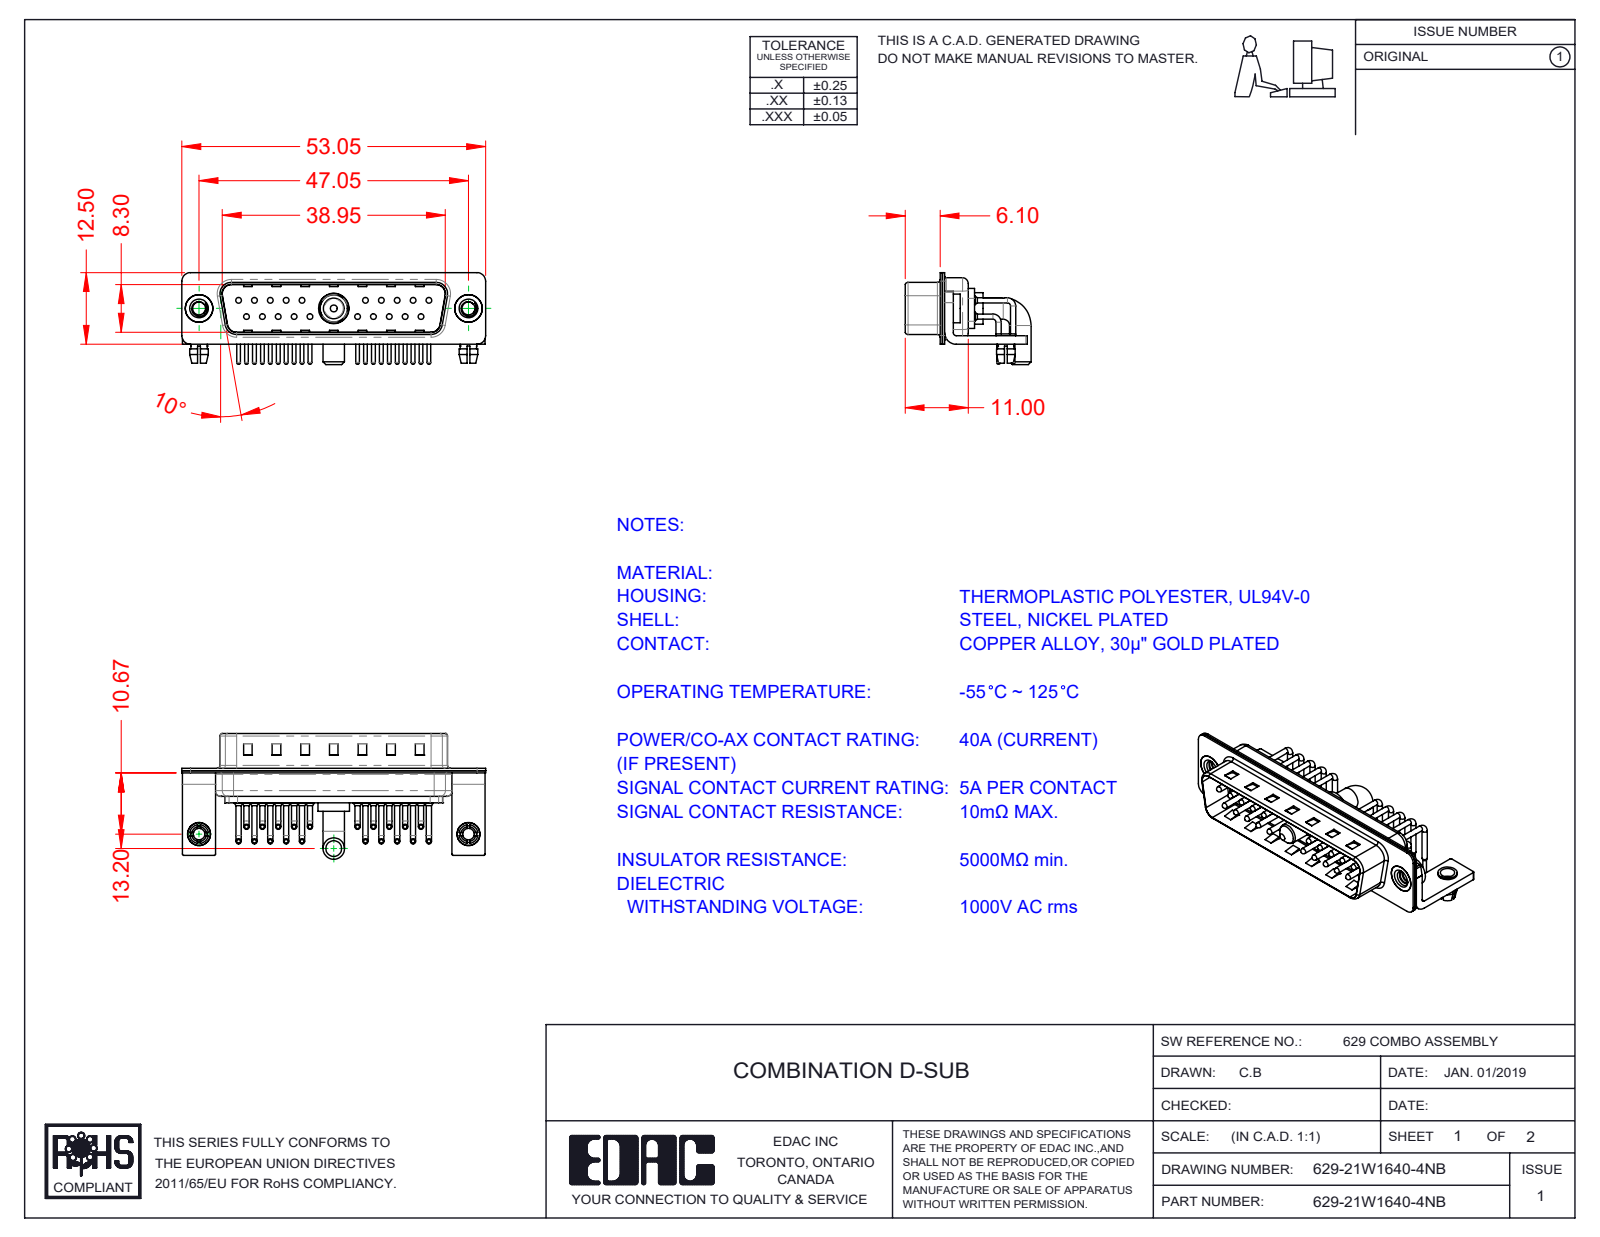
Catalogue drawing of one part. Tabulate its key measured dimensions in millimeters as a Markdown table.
| quantity | value |
| --- | --- |
| part name | 629Combo Contact Row 1; 629Combo Shell Front_25 Contacts; 629Combo Threaded Rivet_2; Power Pin_40A RA (+6 more) |
| STEP written by | SolidWorks 2020 (CONFIG_CONTROL_DESIGN) |
| units | millimeters |
| bodies | 31 solids, 2759 faces (1529 planar, 934 cylindrical, 296 other) |
| overall size | 53.05 × 21.98 × 16.05 |
| volume | 3 439 mm³ |
| surface area | 8 492 mm² |
| round holes (diameter × count) | 2 × 22, 0.75 × 20, 1.6 × 20, 2.26 × 2, 2.5 × 2, 3.2 × 2, 4 × 2, 4.8 × 2, 4.85 × 1, 5.3 × 1 |
| round bosses / shafts (diameter × count) | 0.9 × 40, 1.5 × 20, 1 × 20, 0.65 × 20, 5 × 2, 4.9 × 2, 4 × 2, 3.75 × 2 |
| partial cylindrical surfaces (radius × count) | 1.01 × 20, 0.25 × 16, 1.5 × 16, 2 × 13, 0.5 × 9, 1.6 × 8, 0.6 × 4, 0.65 × 4 |
| main face-to-face distances | 0.4, 0.8, 9.5, 9.1, 1.5, 8.7, 9.9, 0.6, 2.1, 1.2 |
| hole center spacings | 3.16, 2.77, 5.54, 8.31, 5.04, 19.39, 20.97, 22.16 |
